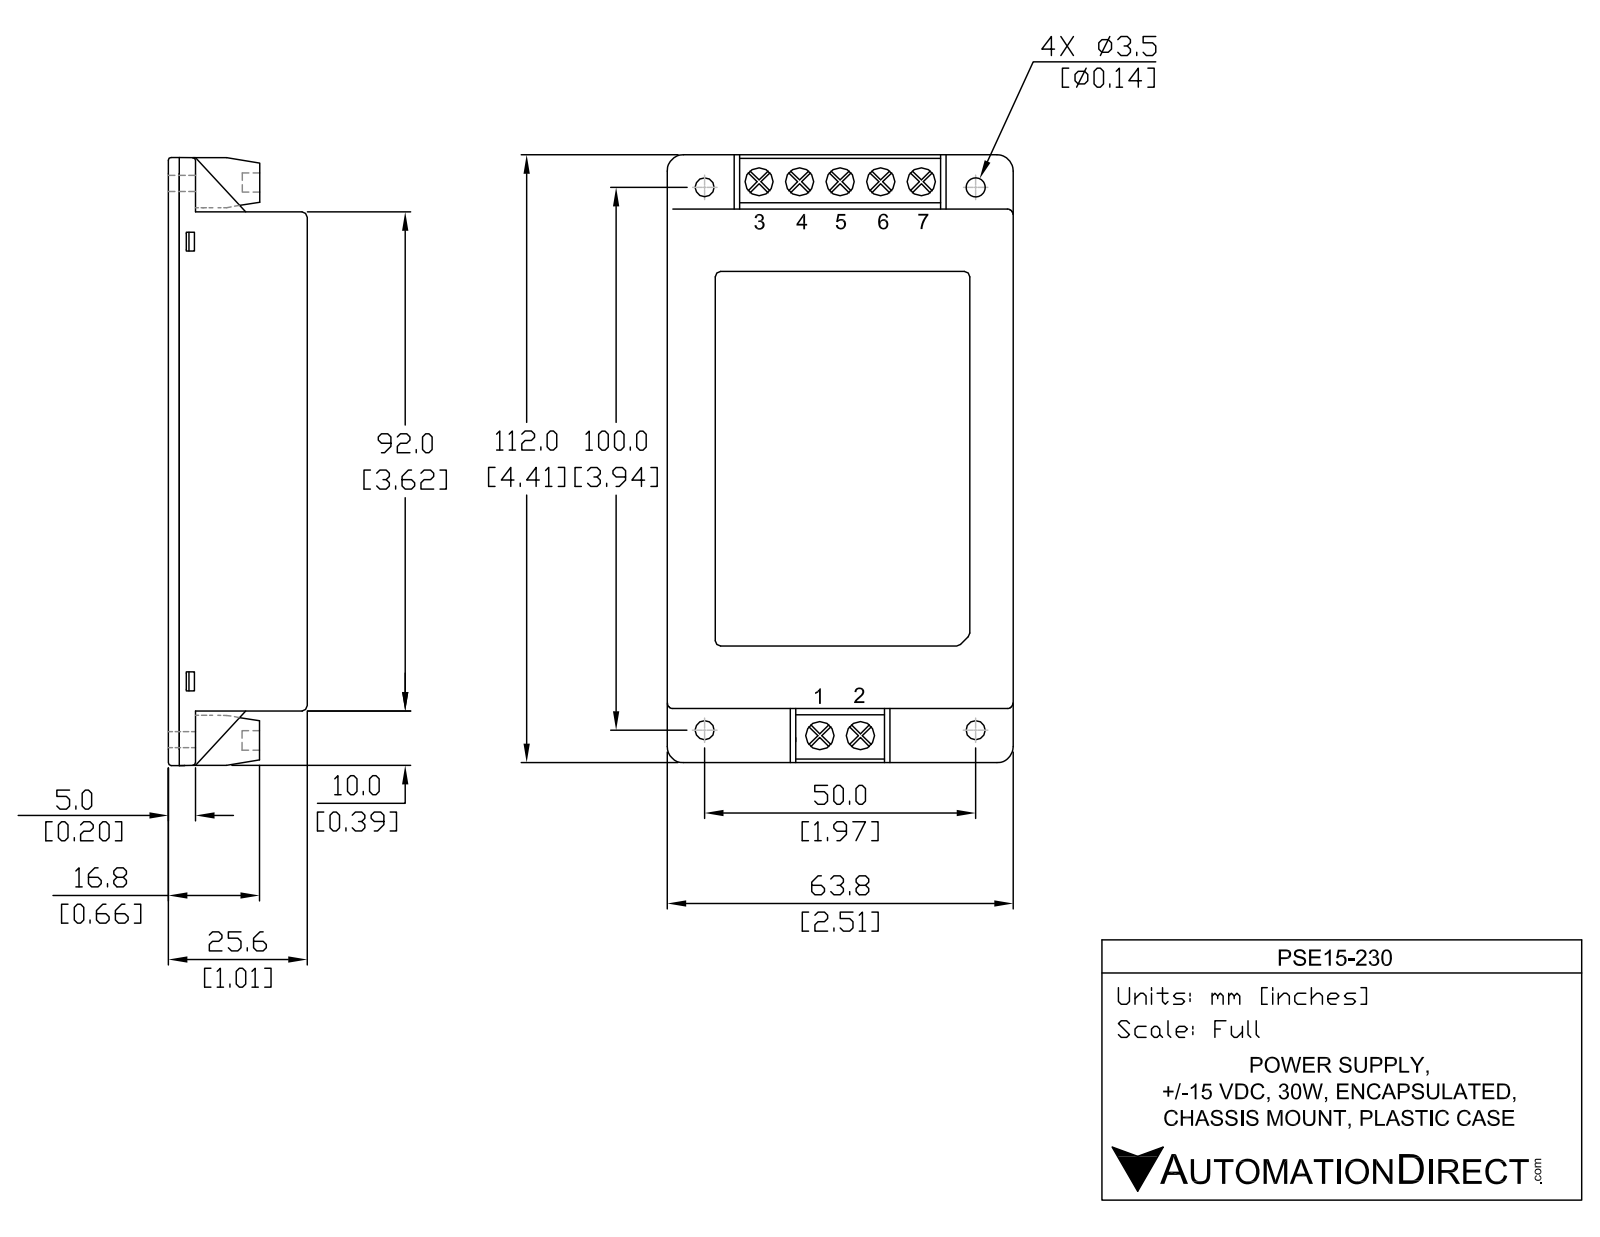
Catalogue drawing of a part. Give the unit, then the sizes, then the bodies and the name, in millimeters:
Units: millimetres
Overall size (bounding box): 112 × 63.8 × 25.7
Round holes (diameter × count): ⌀5.1 ×7, ⌀3.6 ×4
Partial cylindrical surfaces — rounded edges, fillets, slot ends (radius × count): R0.8 ×20, R3.2 ×4
Main face-to-face distances: 2, 2, 23.6, 25.6, 23.6, 25.7, 23.7, 63.8, 91.9, 0.4
Hole centre spacings: 6.6, 13.2, 6.6, 21.7, 28.3, 50, 100.1, 102
Volume: 161 200 mm³ · Surface area: 39 030 mm²
Bodies: 2 solids, 374 faces (246 planar, 62 cylindrical, 66 other)
Part name (STEP PRODUCT): PSE15-230
STEP written by: SolidWorks 2011 (CONFIG_CONTROL_DESIGN)
